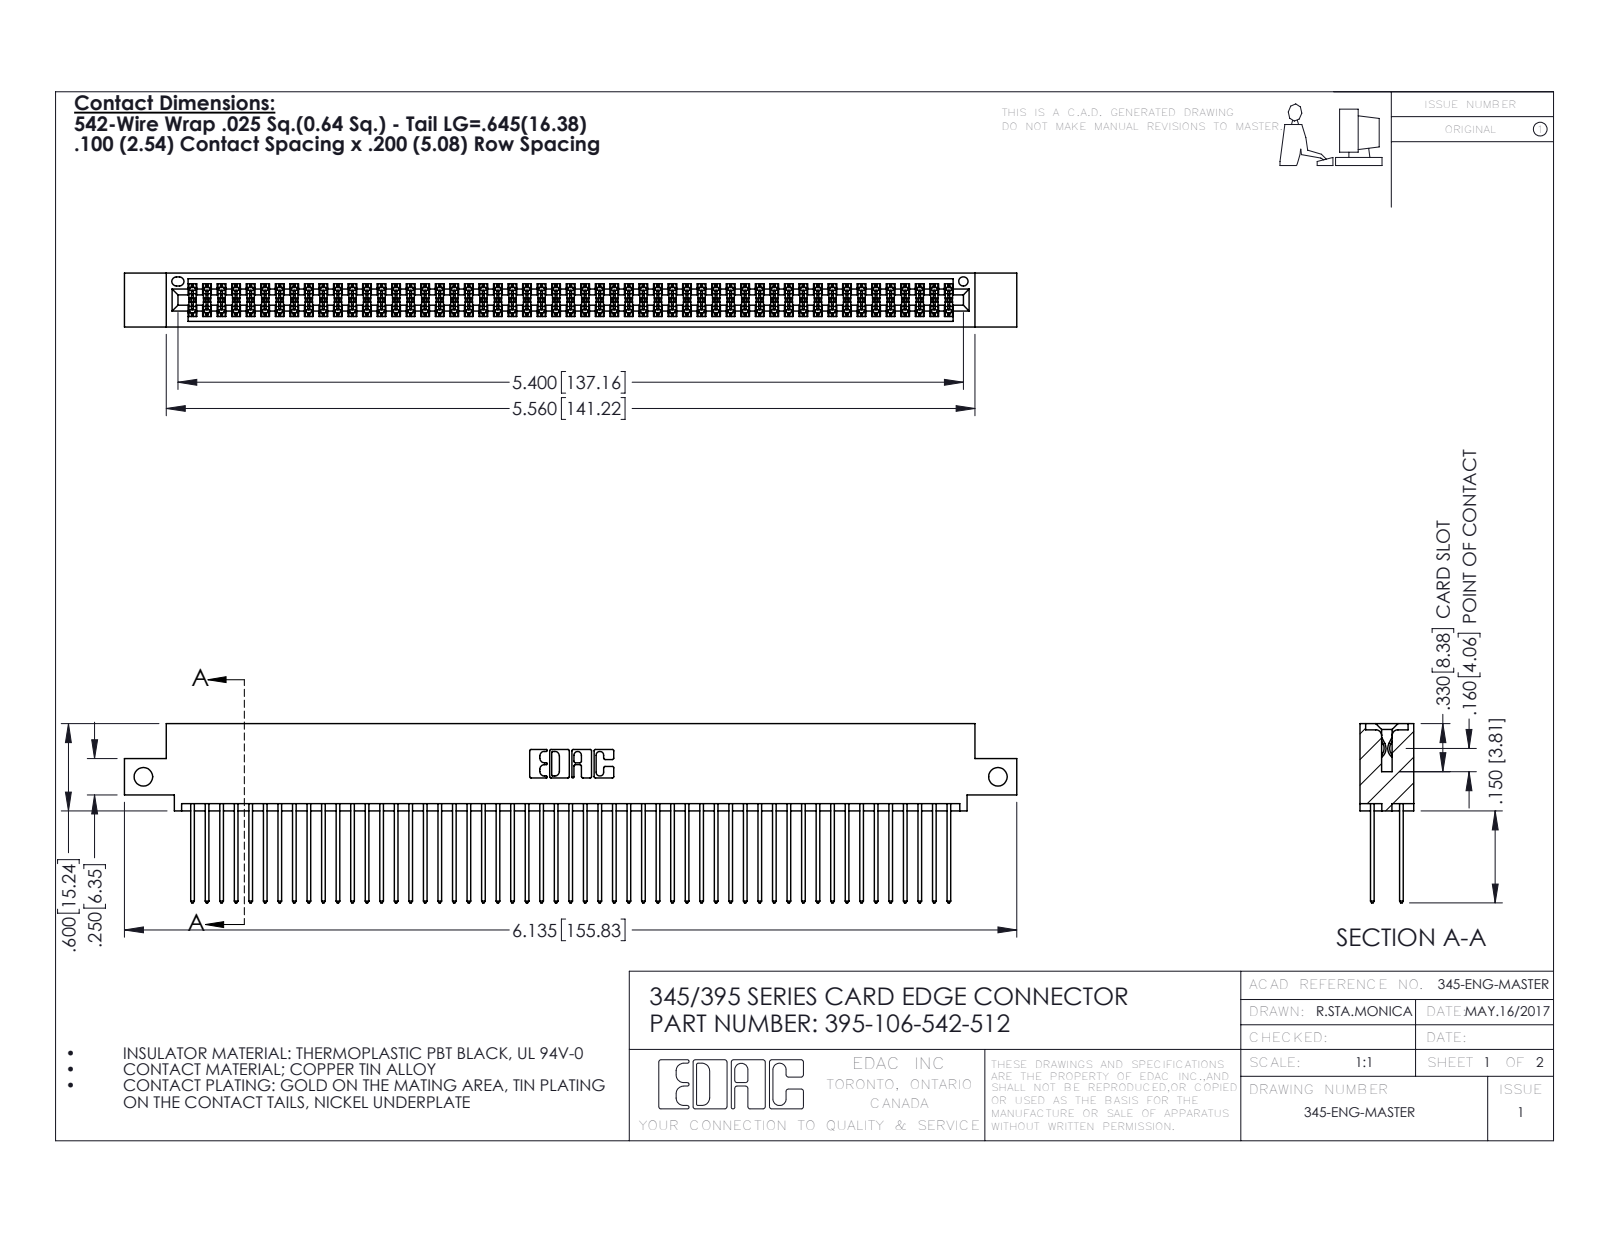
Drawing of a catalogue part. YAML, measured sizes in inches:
part_name: "345-292-001_345-293-142; 395-106-542-512; 345 Part_0.110 Offset - Side Mount"
step_written_by: "SolidWorks 2016 (CONFIG_CONTROL_DESIGN)"
units: inches
bodies: {solids: 107, faces: 5430, planar: 3582, cylindrical: 1848, other: 0}
overall_size: [6.135, 1.232, 0.37]
volume: 0.95
surface_area: 39.52
round_holes:
  - {diameter: 0.128, count: 2}
  - {diameter: 0.064, count: 1}
partial_cylinders:
  - {radius: 0.006, count: 159}
  - {radius: 0.01, count: 106}
  - {radius: 0.01, count: 22}
  - {radius: 0.007, count: 6}
  - {radius: 0.031, count: 6}
  - {radius: 0.026, count: 3}
  - {radius: 0.014, count: 2}
  - {radius: 0.019, count: 2}
face_to_face_distances: [0.298, 0.072, 0.2, 0.098, 0.272, 0.025, 0.225, 0.37, 0.175, 0.149]
hole_center_spacings: [5.875]
